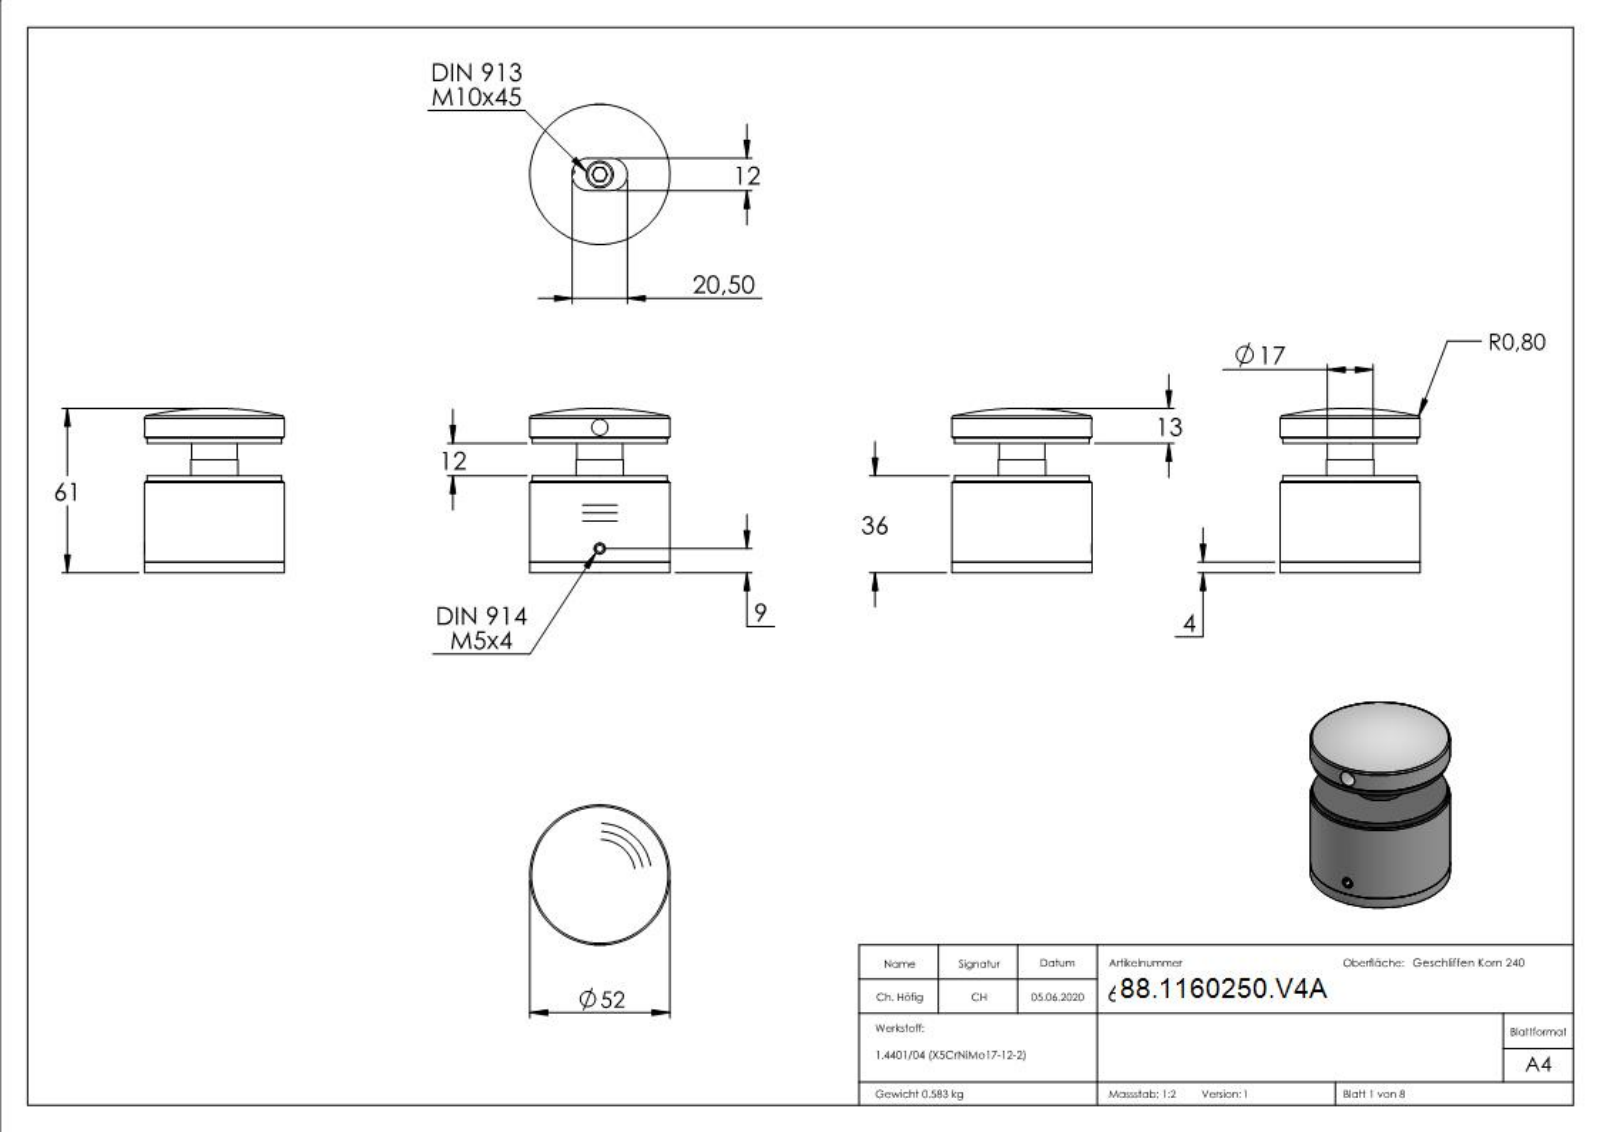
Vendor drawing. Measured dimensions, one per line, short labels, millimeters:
name: 60250-V4A; DIN914; 60250-XXX Teil2_60250-V4A Teil2; 60250-XXX Teil4_60250-XXX Teil4 (+8 more)
written by: SolidWorks 2015 (CONFIG_CONTROL_DESIGN)
unit: mm
bodies: 8 solids, 360 faces (198 planar, 26 cylindrical, 136 other)
size: 120.56 × 70 × 52
volume: 80 320 mm³; area: 38 870 mm²
holes: 2× ⌀4, 1× ⌀4.2, 1× ⌀6, 1× ⌀8.5, 1× ⌀10.5, 1× ⌀14, 1× ⌀36, 1× ⌀43.5, 1× ⌀45.5
bosses: 1× ⌀52, 1× ⌀50, 1× ⌀45, 1× ⌀41, 1× ⌀17.5, 1× ⌀17, 1× ⌀10, 1× ⌀5
rounds: 2× R6
face distances: 16, 14, 2, 12, 24, 4, 30, 34, 36, 50
hole spacings: 16.5, 33, 45
